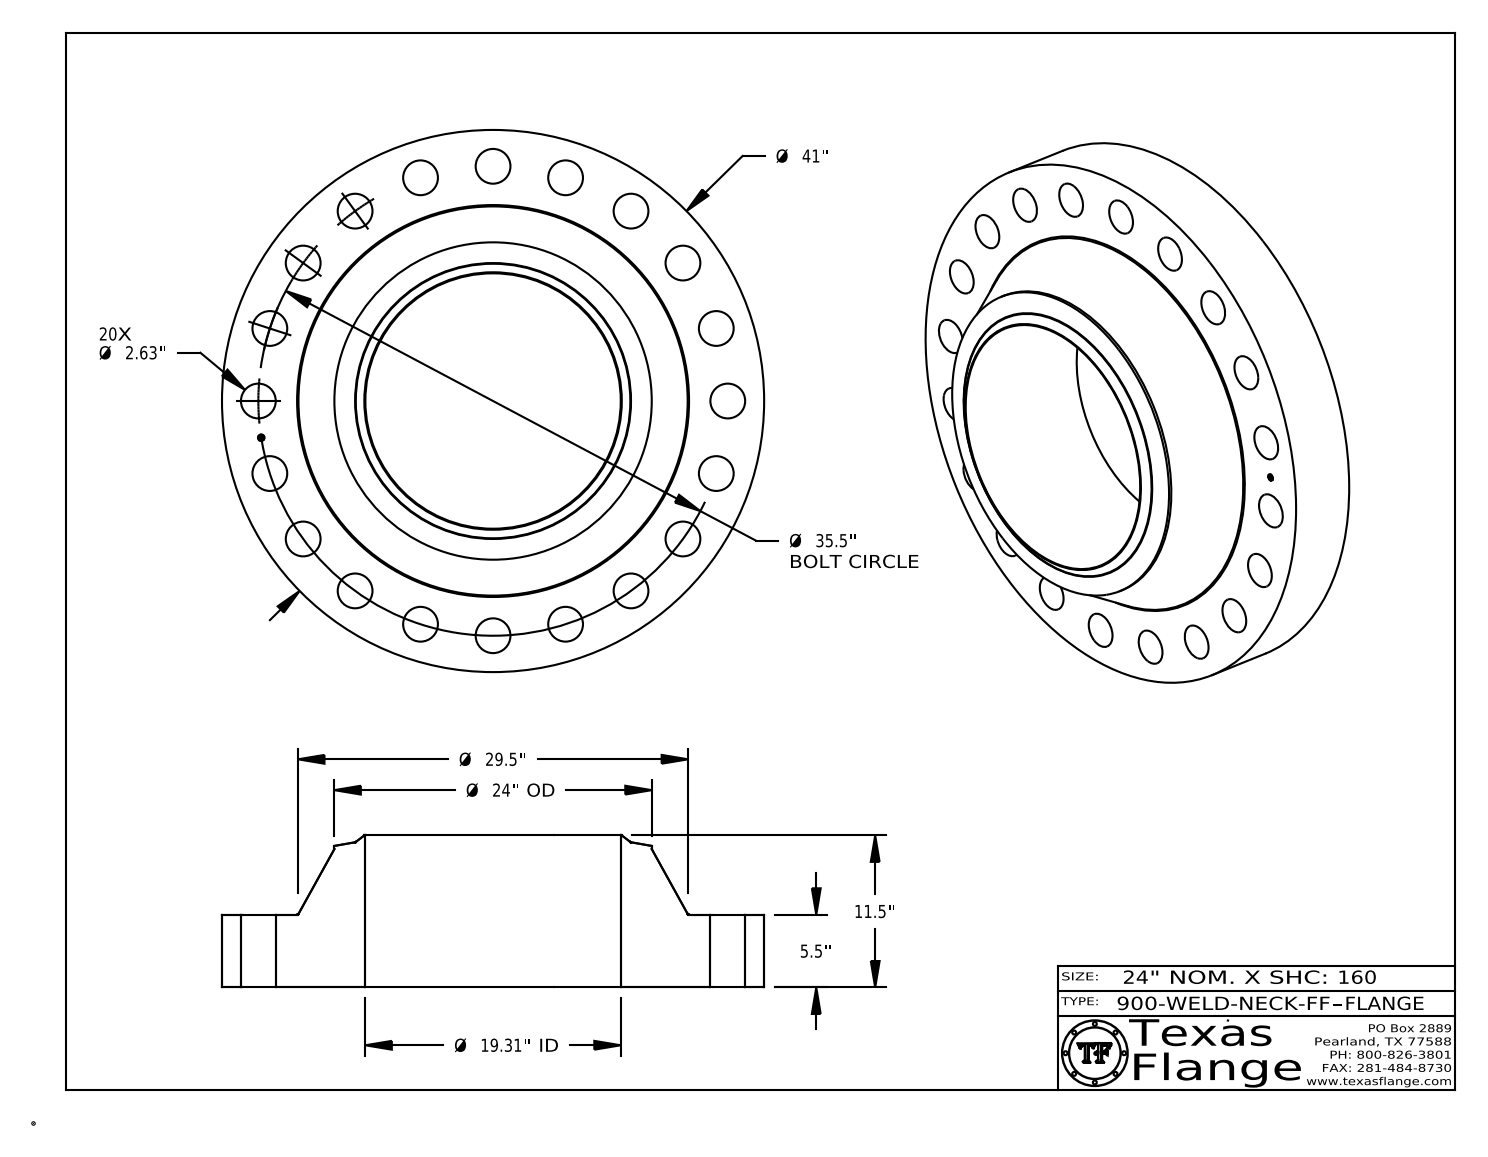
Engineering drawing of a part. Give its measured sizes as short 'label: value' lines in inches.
name: 900-WELD-NECK-FF
written by: CATIA V5 STEP AP214 (AUTOMOTIVE_DESIGN)
unit: in
bodies: 1 solid, 444 faces (368 planar, 66 cylindrical, 10 other)
size: 41 × 41 × 11.5
volume: 6 479 in³; area: 4 428 in²
holes: 20× ⌀2.63, 1× ⌀0.495, 1× ⌀19.312
bosses: 8× ⌀0.03, 1× ⌀41, 1× ⌀24, 1× ⌀0.39
face distances: 5.5, 11.5, 6, 5.485, 0.015, 6.015, 0.148, 0.144, 0.027, 0.096
hole spacings: 17.75, 10.97, 28.72, 31.631, 16.117, 20.866, 25.102, 33.762
